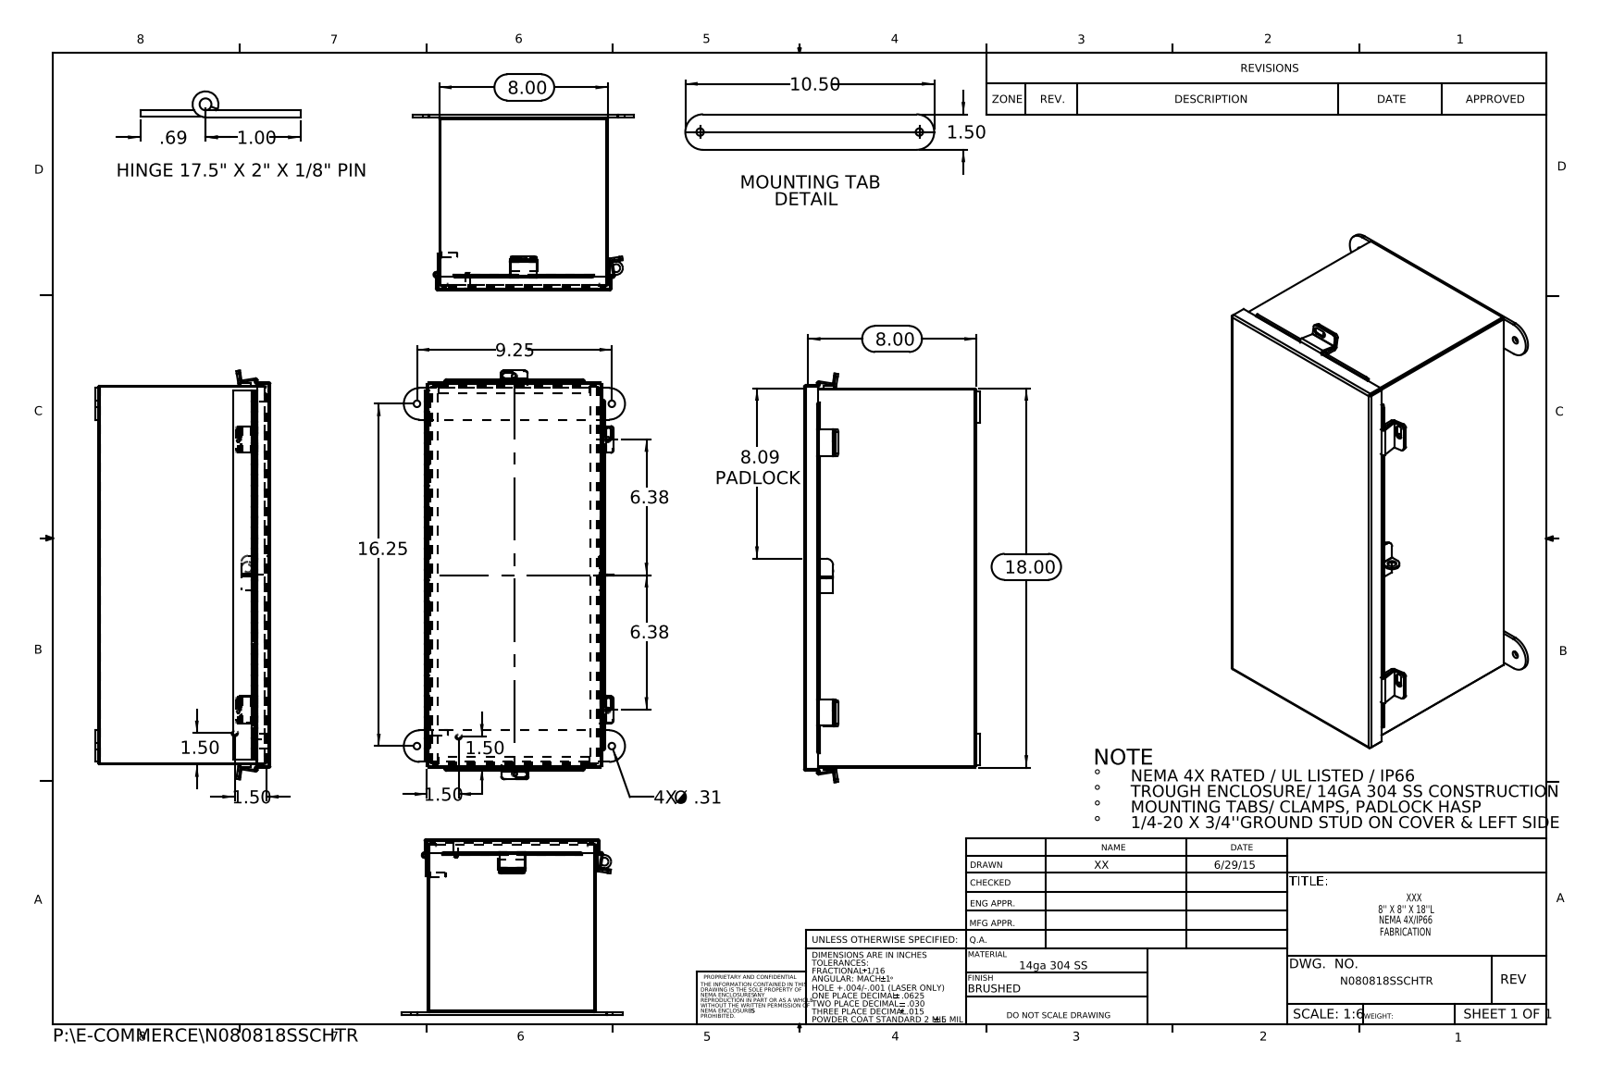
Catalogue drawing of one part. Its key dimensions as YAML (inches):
part_name: "N080818SSCHTR; N080818SSCHTR Hinge Body Side; N080818SSCHTR JIC Enclosure Template; HW-CLH-JH-20104_DefaultSM-FLAT-PATTERN (+8 more)"
step_written_by: "SolidWorks 2015 (CONFIG_CONTROL_DESIGN)"
units: inches
bodies: {solids: 20, faces: 742, planar: 459, cylindrical: 263, other: 20}
overall_size: [19.407, 10.5, 8.337]
volume: 63.9
surface_area: 1698
round_holes:
  - {diameter: 0.25, count: 4}
  - {diameter: 0.313, count: 4}
  - {diameter: 0.375, count: 2}
  - {diameter: 0.125, count: 1}
round_bosses_or_shafts:
  - {diameter: 0.315, count: 2}
  - {diameter: 0.236, count: 2}
  - {diameter: 0.273, count: 1}
  - {diameter: 0.25, count: 1}
partial_cylinders:
  - {radius: 0.125, count: 15}
  - {radius: 0.009, count: 12}
  - {radius: 0.013, count: 11}
  - {radius: 0.088, count: 11}
  - {radius: 0.133, count: 8}
  - {radius: 0.083, count: 6}
  - {radius: 0.1, count: 6}
  - {radius: 0.75, count: 4}
face_to_face_distances: [0.075, 7.925, 8.128, 8, 7.85, 8.203, 8.053, 17.925, 17.85, 18]
hole_center_spacings: [9.25, 16.25, 18.698, 8.541, 12.85]
